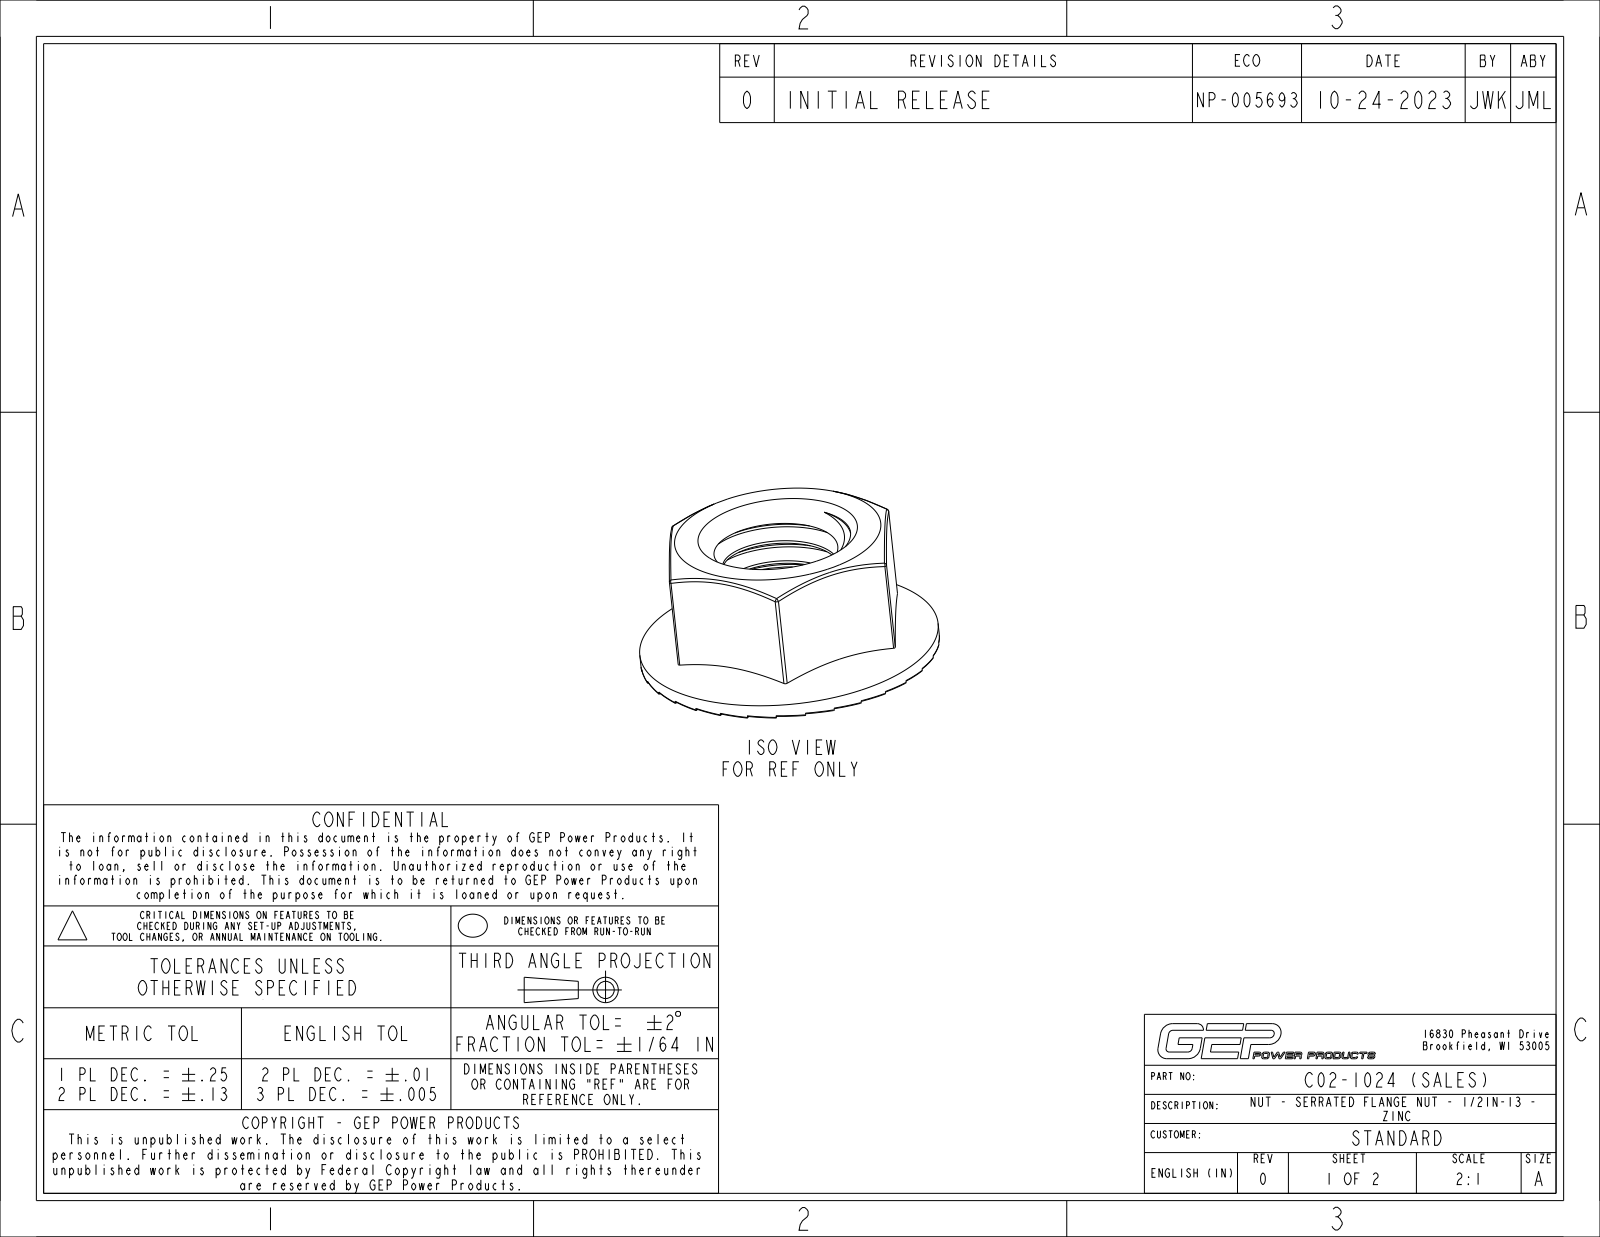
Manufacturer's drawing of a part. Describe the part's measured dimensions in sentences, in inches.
The part is named "C02-1024_NCF; C02-1024_SALES_NCF_ASM". Its 3-D file was written by "CREO PARAMETRIC BY PTC INC, 2017110 (CONFIG_CONTROL_DESIGN)". It is 1 solid with 276 faces: 40 planar, 84 cylindrical and 152 other. Overall it measures 1.031 by 1.031 by 0.453 inches. Its volume is 0.166 cubic inches and its surface area 3.35 square inches. Round holes: 1 of diameter 0.5. Round bosses or shafts: 1 of diameter 1.031. Partial cylindrical surfaces (rounded edges, fillets, slot ends): 32 of radius 0.116, 32 of radius 0.218, 6 of radius 0.011. The main face-to-face distances are 0.75, 0.441.
